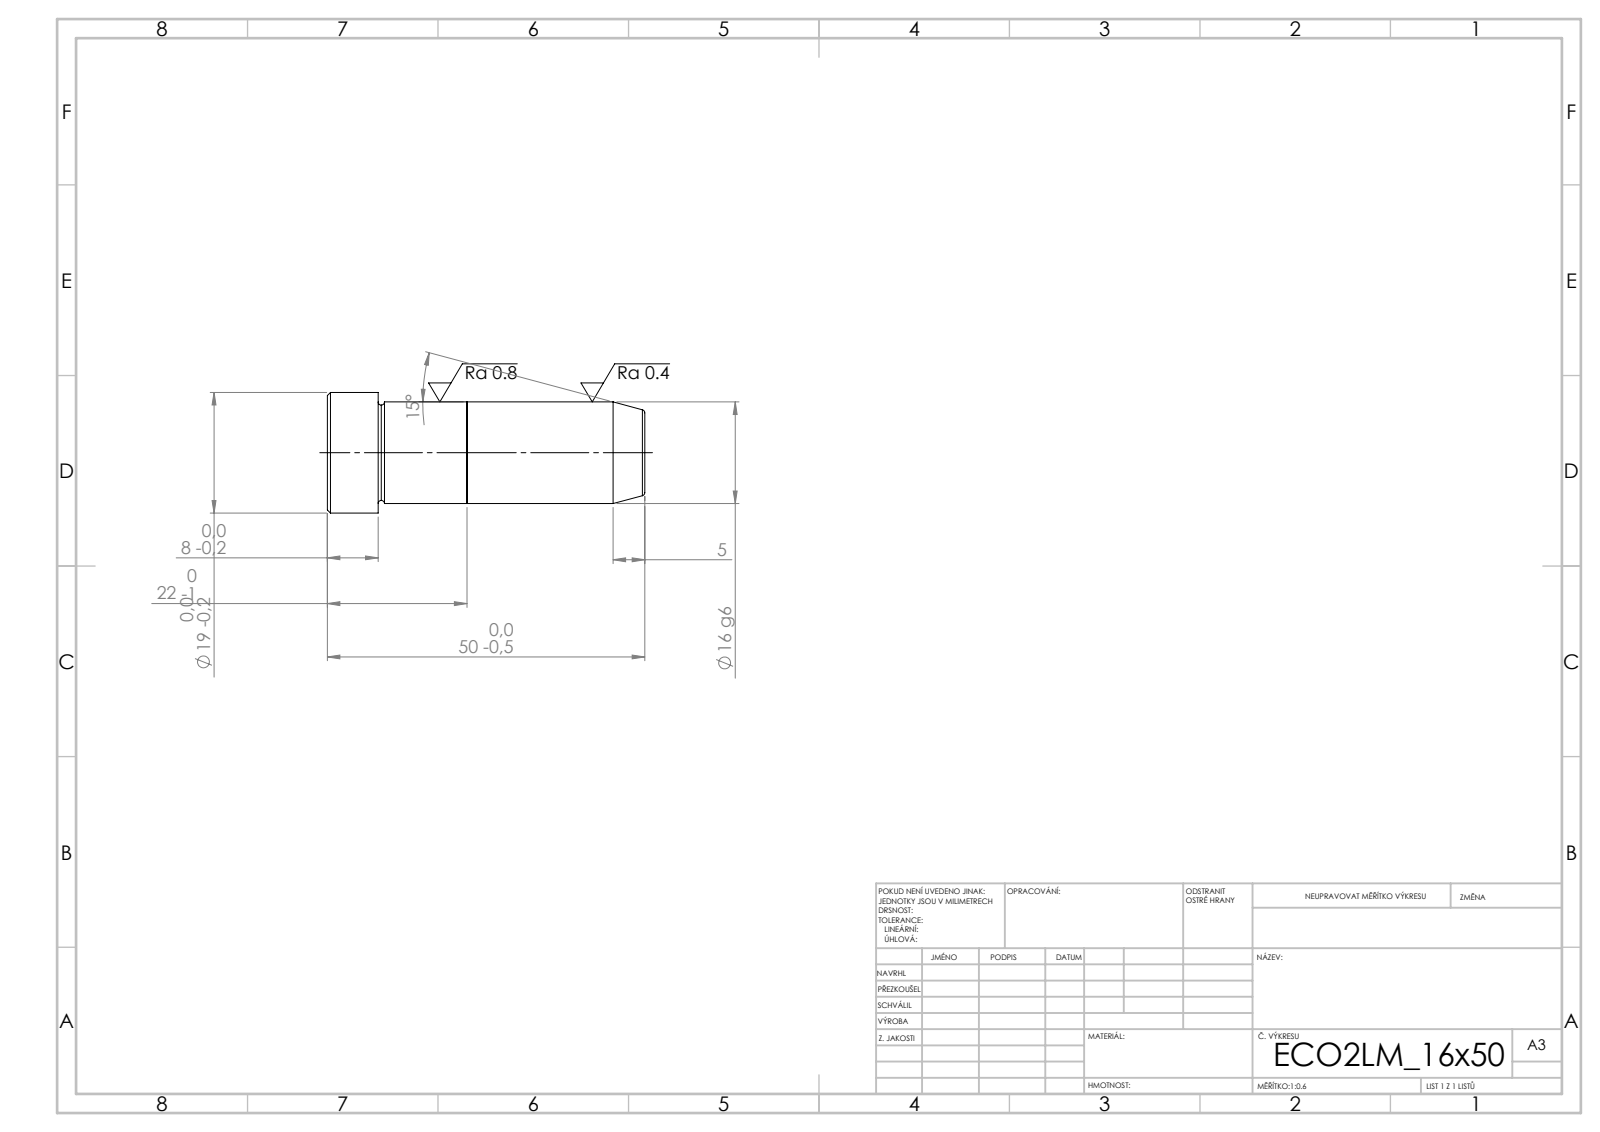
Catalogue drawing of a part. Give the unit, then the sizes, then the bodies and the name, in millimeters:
Units: millimetres
Overall size (bounding box): 50 × 19 × 19
Round bosses / shafts (diameter × count): ⌀19 ×1, ⌀16 ×1
Main face-to-face distances: 22, 28, 50, 42, 14, 8
Volume: 10 526 mm³ · Surface area: 3 486 mm²
Bodies: 2 solids, 21 faces (5 planar, 6 cylindrical, 10 other)
STEP written by: SolidWorks 2019 (CONFIG_CONTROL_DESIGN)
